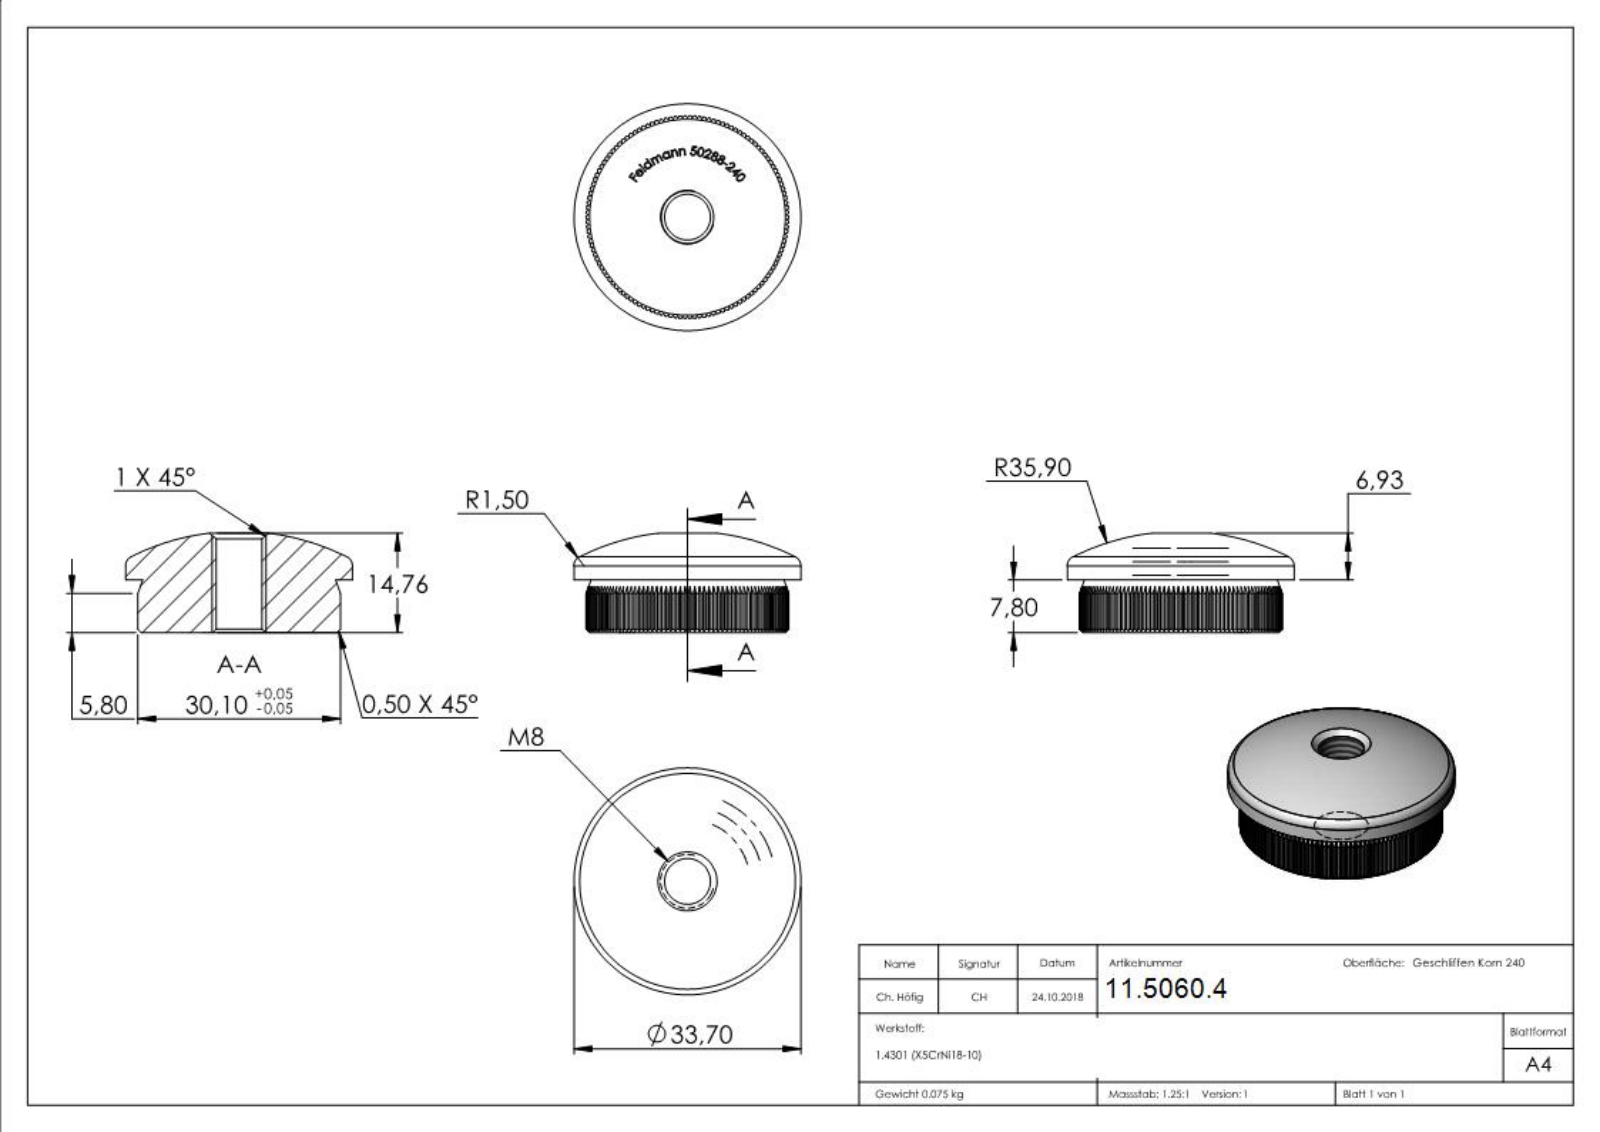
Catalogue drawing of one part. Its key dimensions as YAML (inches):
part_name: "50288-240"
step_written_by: "SolidWorks 2015 (CONFIG_CONTROL_DESIGN)"
units: inches
bodies: {solids: 1, faces: 633, planar: 392, cylindrical: 134, other: 107}
overall_size: [1.327, 1.327, 0.58]
volume: 0.576
surface_area: 5.363
round_holes:
  - {diameter: 0.268, count: 1}
round_bosses_or_shafts:
  - {diameter: 1.327, count: 1}
partial_cylinders:
  - {radius: 0.593, count: 1}
face_to_face_distances: [0.307, 0.579, 0.58, 0.578, 0.303, 0.026, 0.021, 0.301, 0.278, 0.026]
